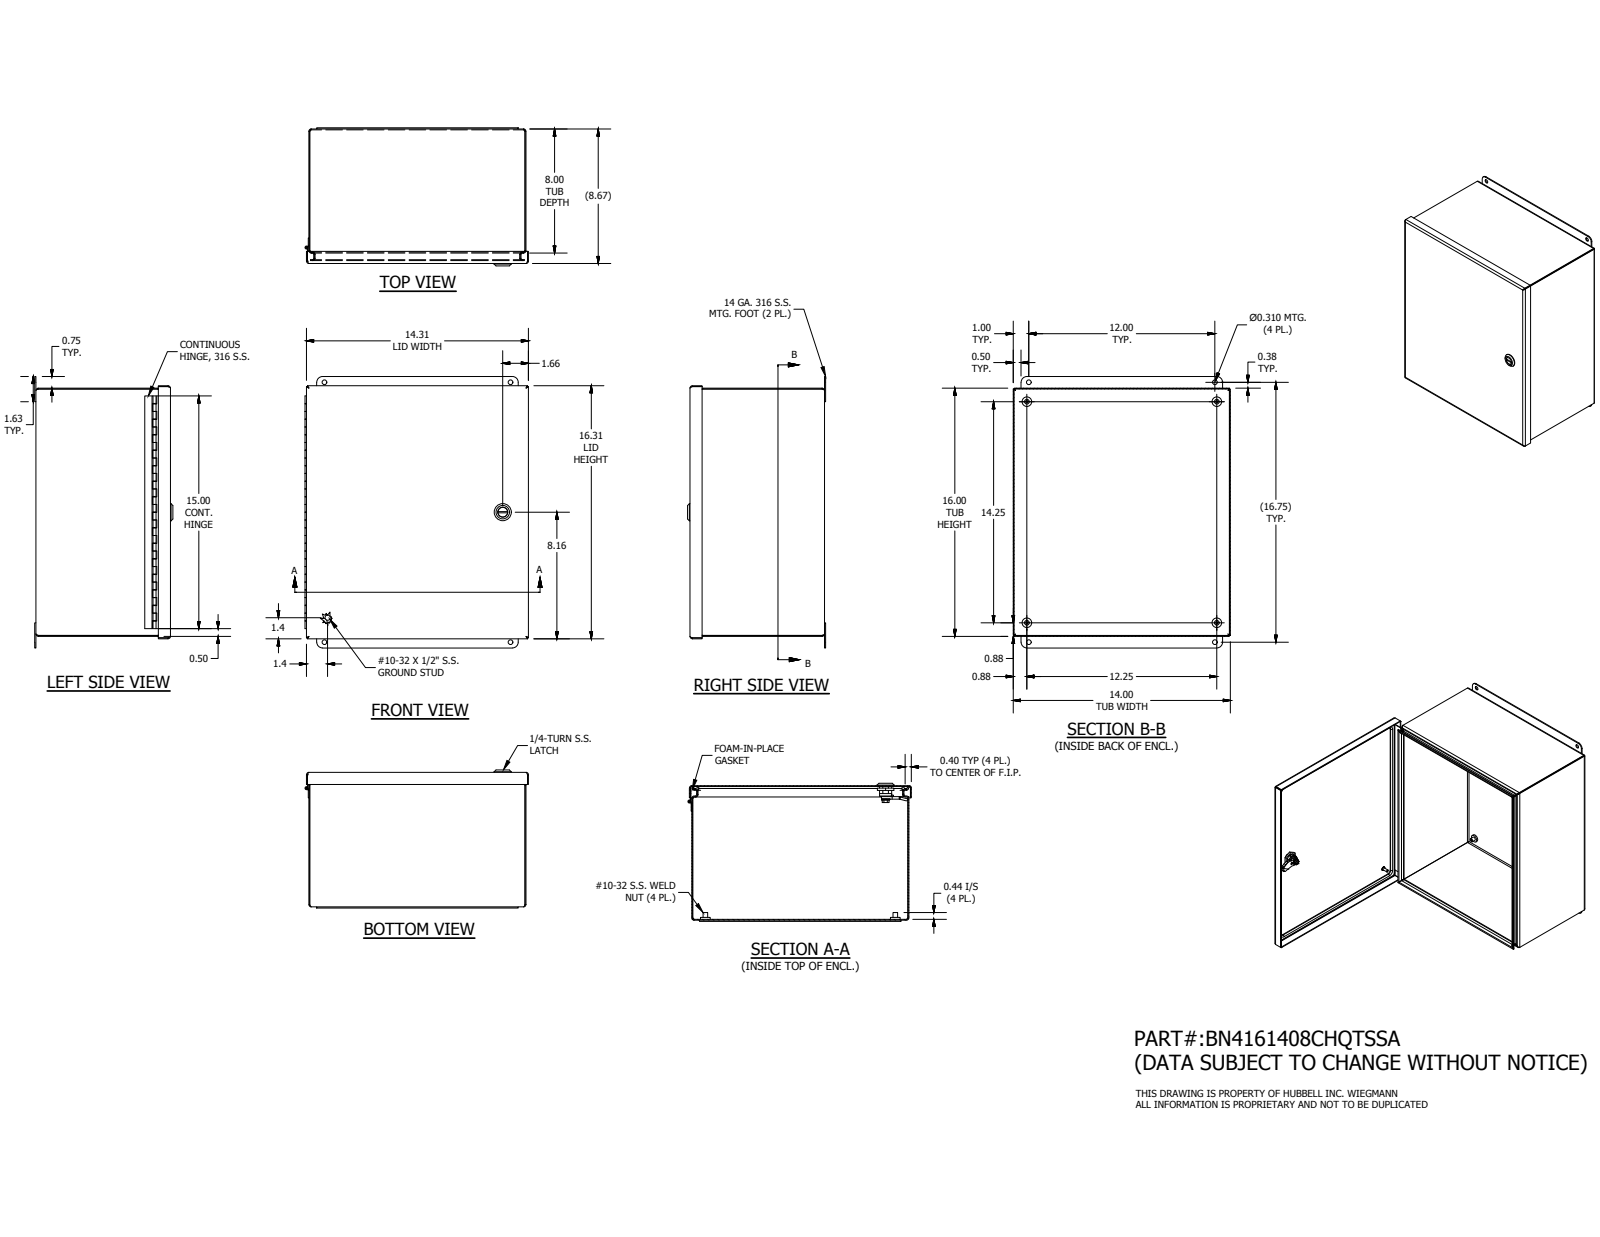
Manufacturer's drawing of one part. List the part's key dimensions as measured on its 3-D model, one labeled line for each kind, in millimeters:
Part name (STEP PRODUCT): BN41614CHQTSSALID; 16x14; 348132; 32886LH (+8 more)
STEP written by: Autodesk Inventor 2016 (AUTOMOTIVE_DESIGN)
Units: millimetres
Bodies: 21 solids, 711 faces (390 planar, 224 cylindrical, 97 other)
Overall size (bounding box): 444.5 × 366.06 × 226.19
Volume: 1 157 000 mm³ · Surface area: 1 471 000 mm²
Round holes (diameter × count): ⌀3.96 ×4, ⌀7.87 ×4, ⌀2.96 ×1, ⌀5 ×1, ⌀8 ×1, ⌀10 ×1, ⌀10.2 ×1, ⌀16.1 ×1, ⌀20.38 ×1
Round bosses / shafts (diameter × count): ⌀15.88 ×4, ⌀7.62 ×4, ⌀28 ×1, ⌀19.8 ×1, ⌀16 ×1, ⌀15.2 ×1, ⌀13.5 ×1, ⌀12.8 ×1
Partial cylindrical surfaces — rounded edges, fillets, slot ends (radius × count): R2.38 ×20, R3.88 ×20, R3.17 ×16, R0.5 ×8, R4 ×4, R9.53 ×4, R2.31 ×2, R6.45 ×1
Main face-to-face distances: 1.5, 1.49, 218.79, 220.28, 217.29, 218.78, 404.9, 354.11, 355.6, 352.61
Hole centre spacings: 31.91, 393.71, 499.85, 304.8, 309.6, 309.61, 311.15, 346.32
